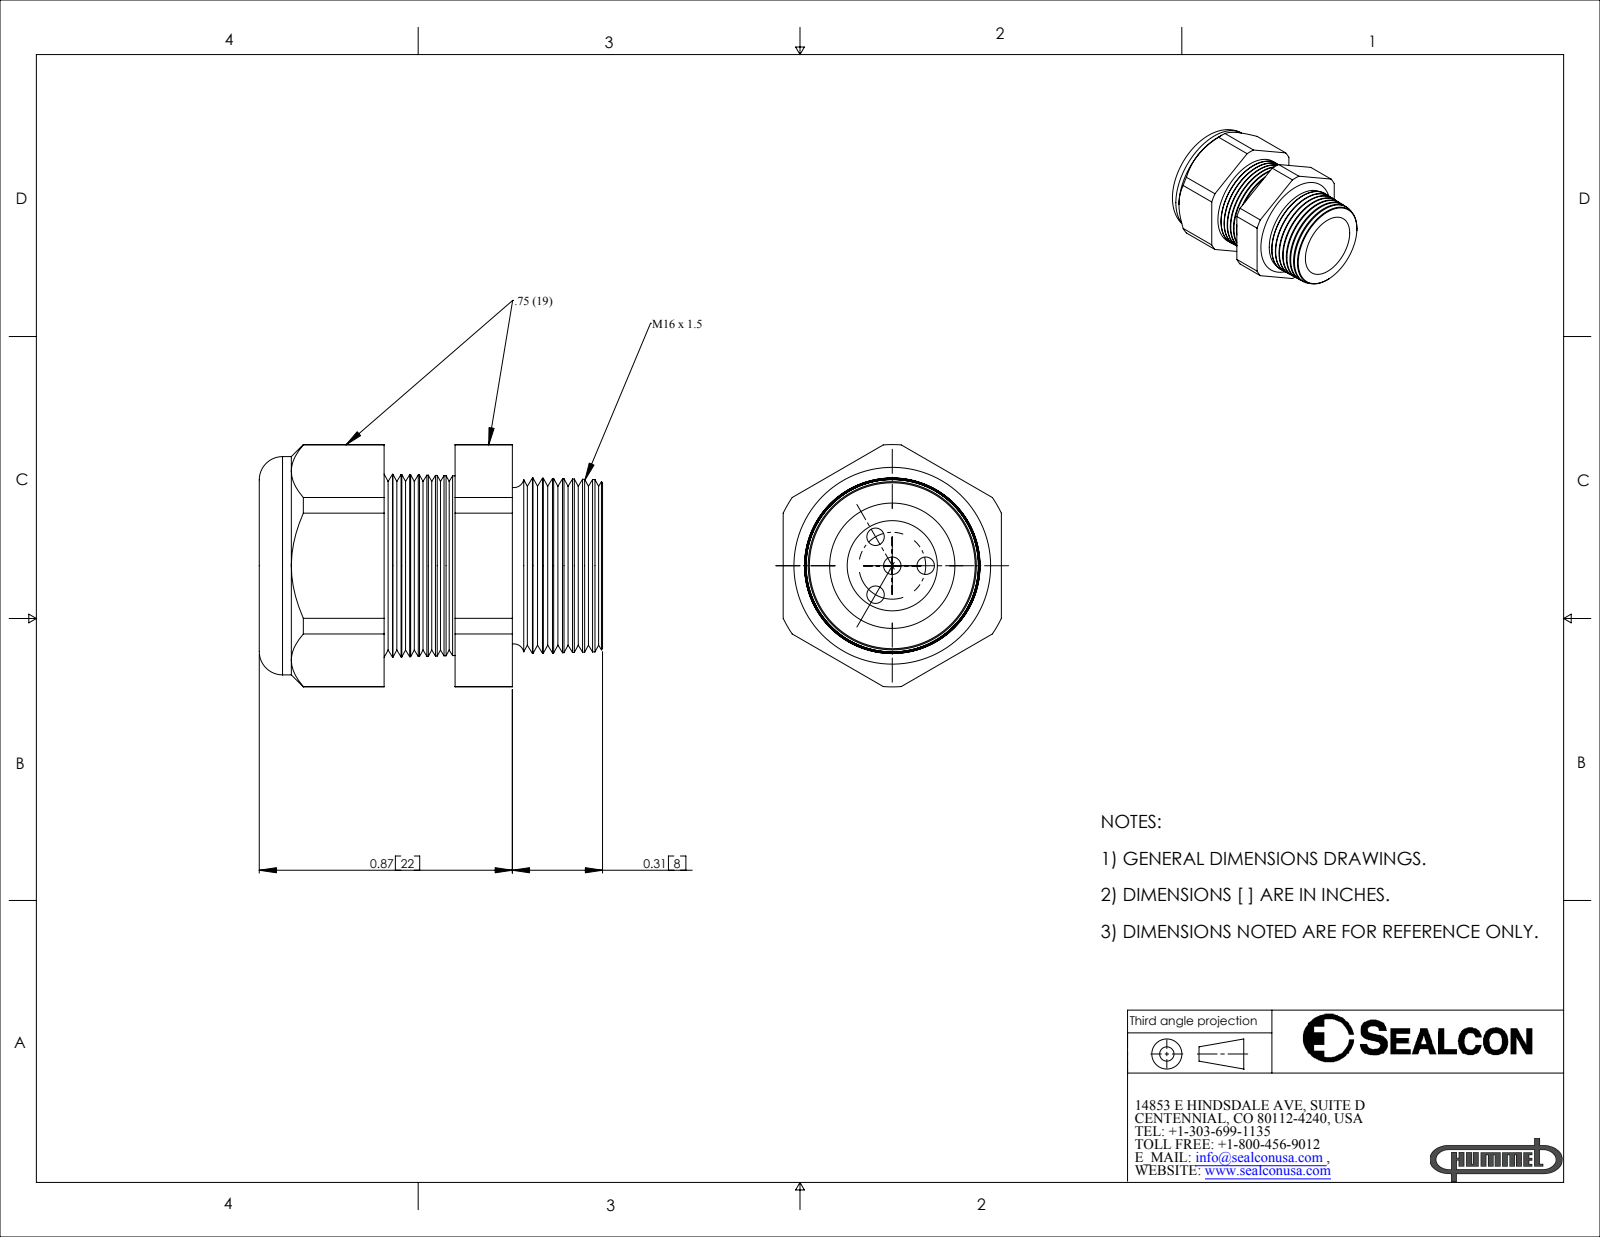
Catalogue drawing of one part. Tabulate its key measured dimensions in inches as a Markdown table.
| quantity | value |
| --- | --- |
| part name | CD16M1-BK |
| STEP written by | SolidWorks 2007 (CONFIG_CONTROL_DESIGN) |
| units | inches |
| bodies | 2 solids, 158 faces (20 planar, 28 cylindrical, 110 other) |
| overall size | 1.18 × 0.833 × 0.75 |
| volume | 0.336 in³ |
| surface area | 6.185 in² |
| round holes (diameter × count) | 0.06 × 4, 0.29 × 1, 0.31 × 1 |
| round bosses / shafts (diameter × count) | 0.75 × 1 |
| partial cylindrical surfaces (radius × count) | 0.416 × 1 |
| main face-to-face distances | 0.75, 0.673, 0.75, 0.429, 0.244, 0.87, 0.441, 0.197, 1.18, 0.751 |
| hole center spacings | 0.115, 0.199 |
